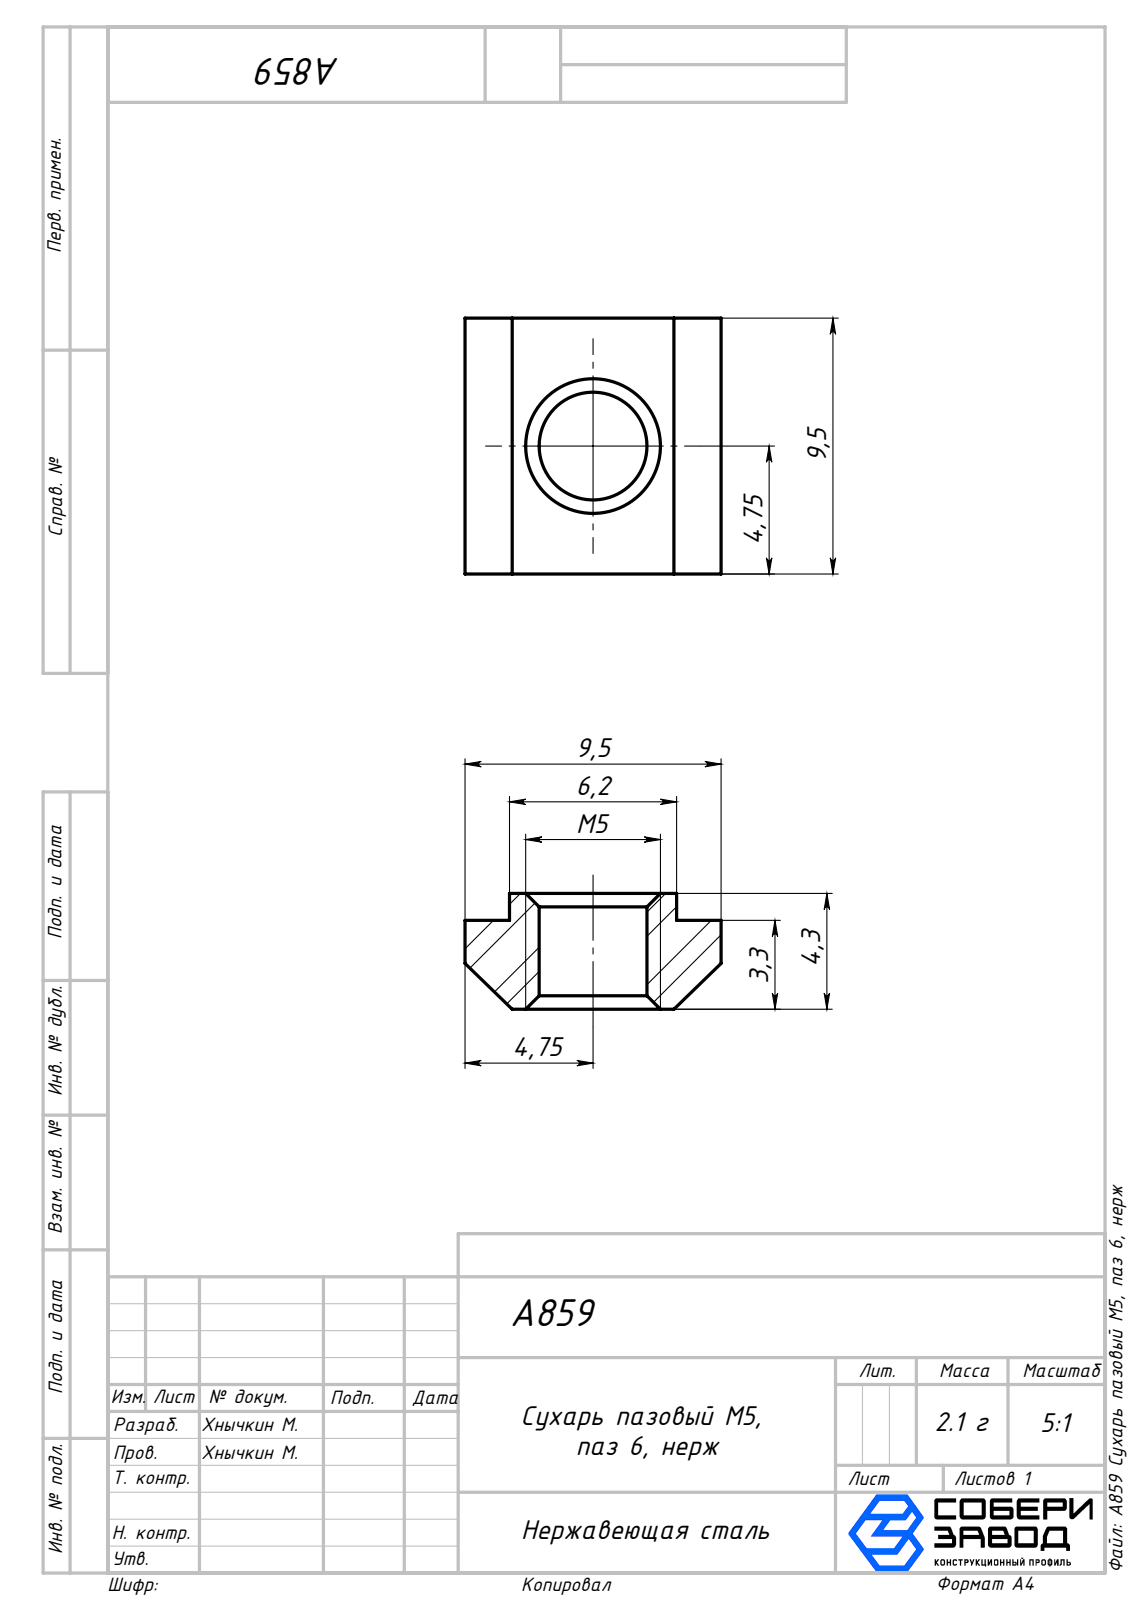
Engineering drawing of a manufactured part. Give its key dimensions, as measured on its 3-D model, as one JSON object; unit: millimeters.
{"part_name": "A859 Сухарь пазовый М5, паз 6, нерж", "step_written_by": "SolidWorks 2025 (AUTOMOTIVE_DESIGN)", "units": "millimeters", "bodies": {"solids": 1, "faces": 18, "planar": 12, "cylindrical": 2, "other": 4}, "overall_size": [9.5, 9.5, 4.3], "volume_mm3": 271, "surface_area_mm2": 334, "round_holes": [[4, 1]], "face_to_face_distances": [9.5, 4.3, 3.3, 1, 1.65, 7.85, 6.2]}
